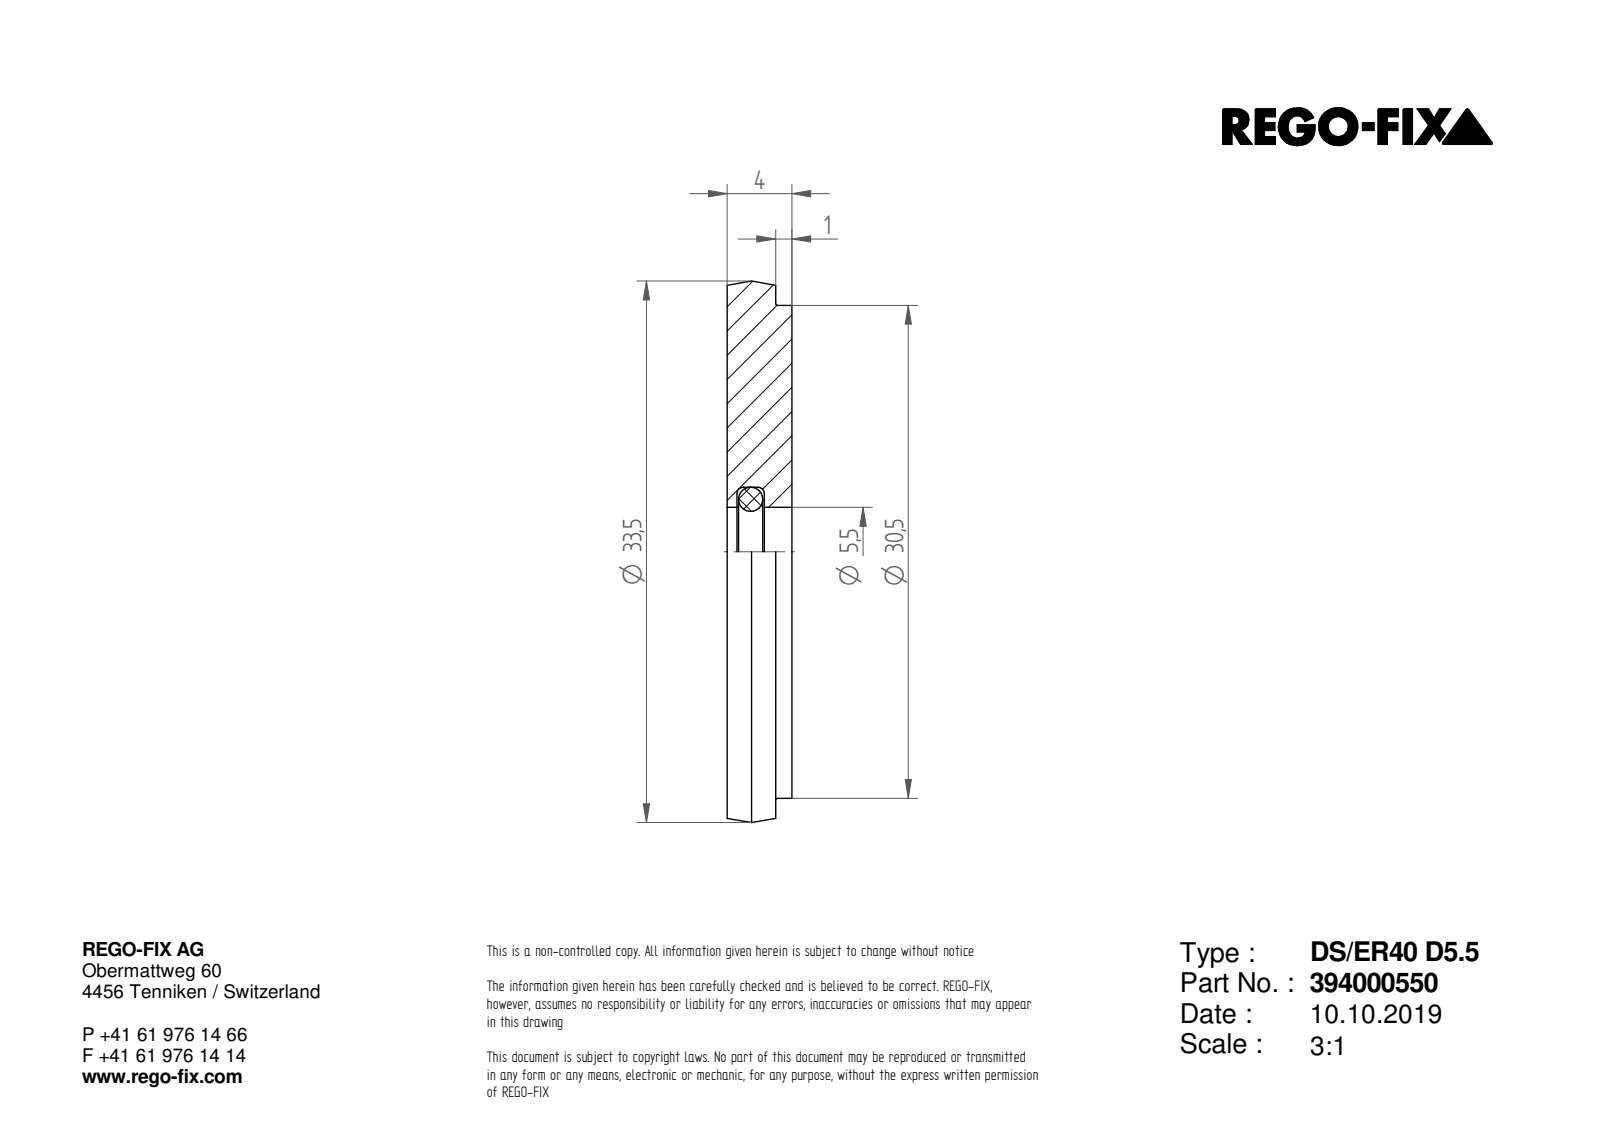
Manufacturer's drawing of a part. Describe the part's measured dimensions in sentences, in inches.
The part is named "NOCUT". Its 3-D file was written by "SIEMENS PLM Software Solid Edge ST10 (AUTOMOTIVE_DESIGN)". It is 1 solid with 7 faces: 3 planar, 3 cylindrical and 1 other. Overall it measures 1.319 by 1.319 by 0.157 inches. Its volume is 0.2 cubic inches and its surface area 3.398 square inches. Round holes: 1 of diameter 0.217. Round bosses or shafts: 1 of diameter 1.319, 1 of diameter 1.201. The main face-to-face distances are 0.157, 0.039, 0.118.
